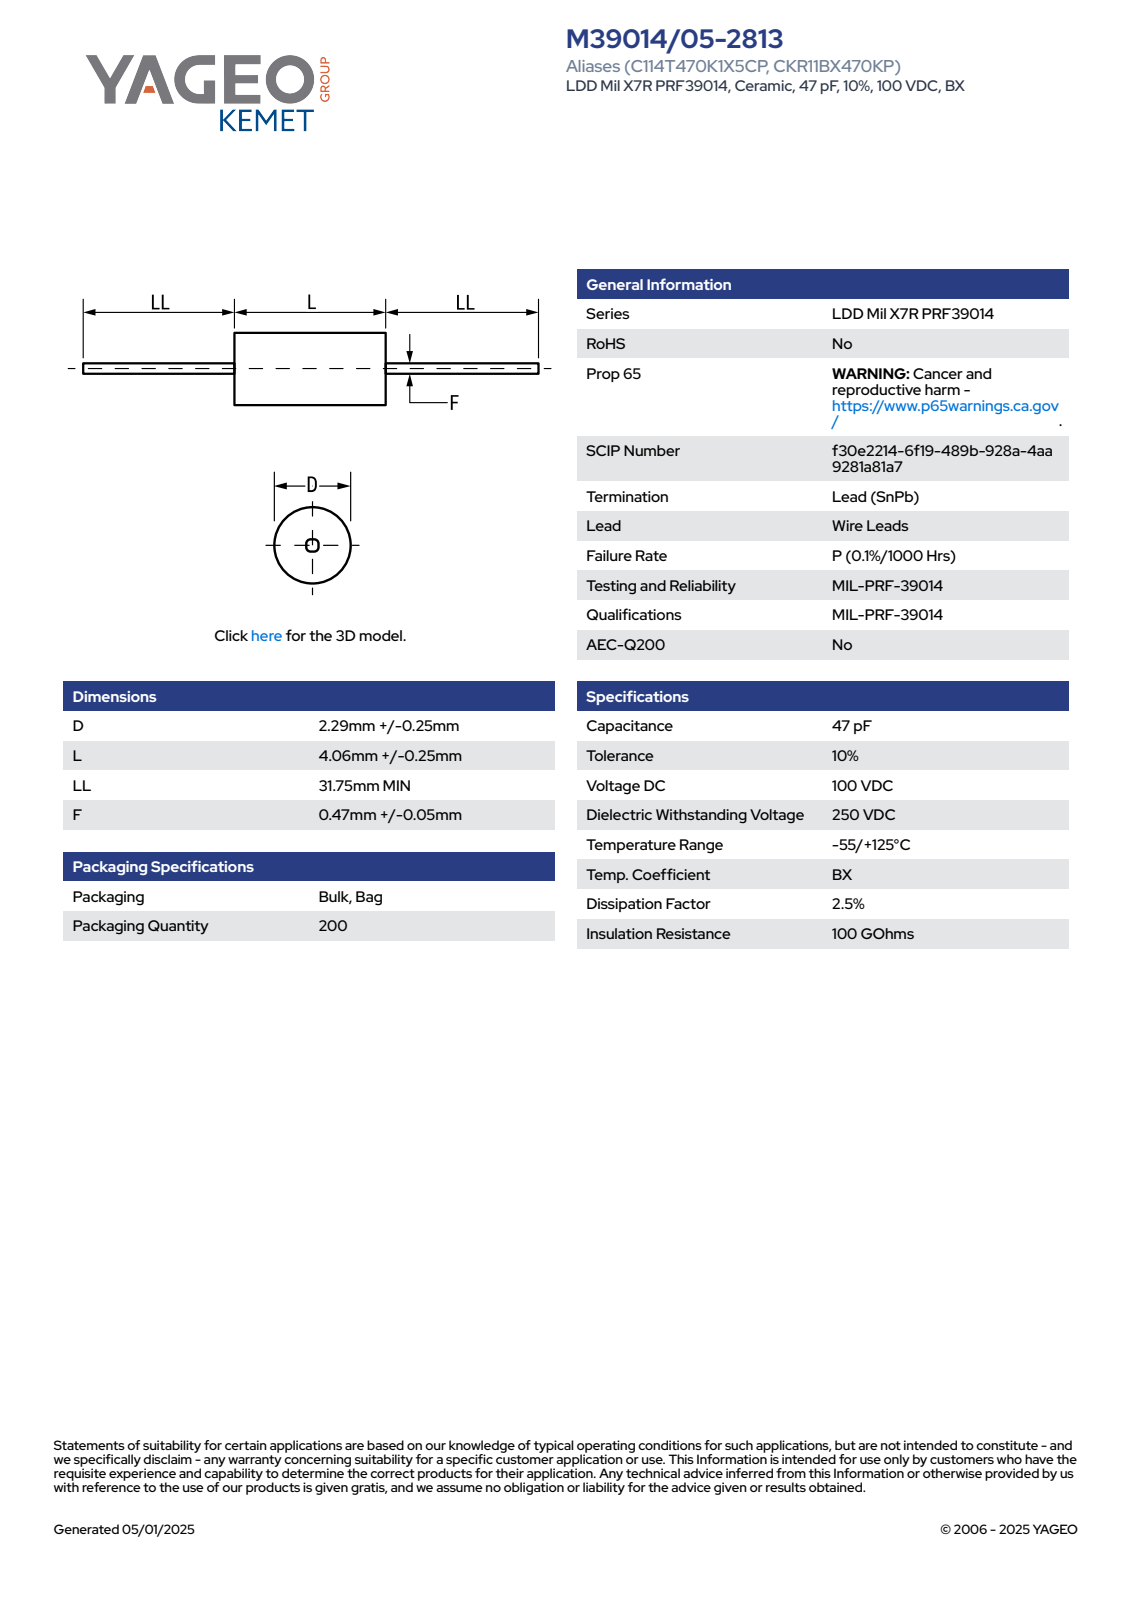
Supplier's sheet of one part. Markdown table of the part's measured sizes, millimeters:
| quantity | value |
| --- | --- |
| part name | CCA_AXM_C114_D2.54L4.31LL38.1F0.43 |
| STEP written by | SolidWorks 2014 (AUTOMOTIVE_DESIGN) |
| units | millimeters |
| bodies | 1 solid, 66 faces (26 planar, 9 cylindrical, 31 other) |
| overall size | 80.51 × 2.54 × 2.54 |
| volume | 33 mm³ |
| surface area | 148 mm² |
| round bosses / shafts (diameter × count) | 2.54 × 1, 0.43 × 1 |
| partial cylindrical surfaces (radius × count) | 1.26 × 1 |
| main face-to-face distances | 4.3, 38.11, 42.41, 80.52 |
